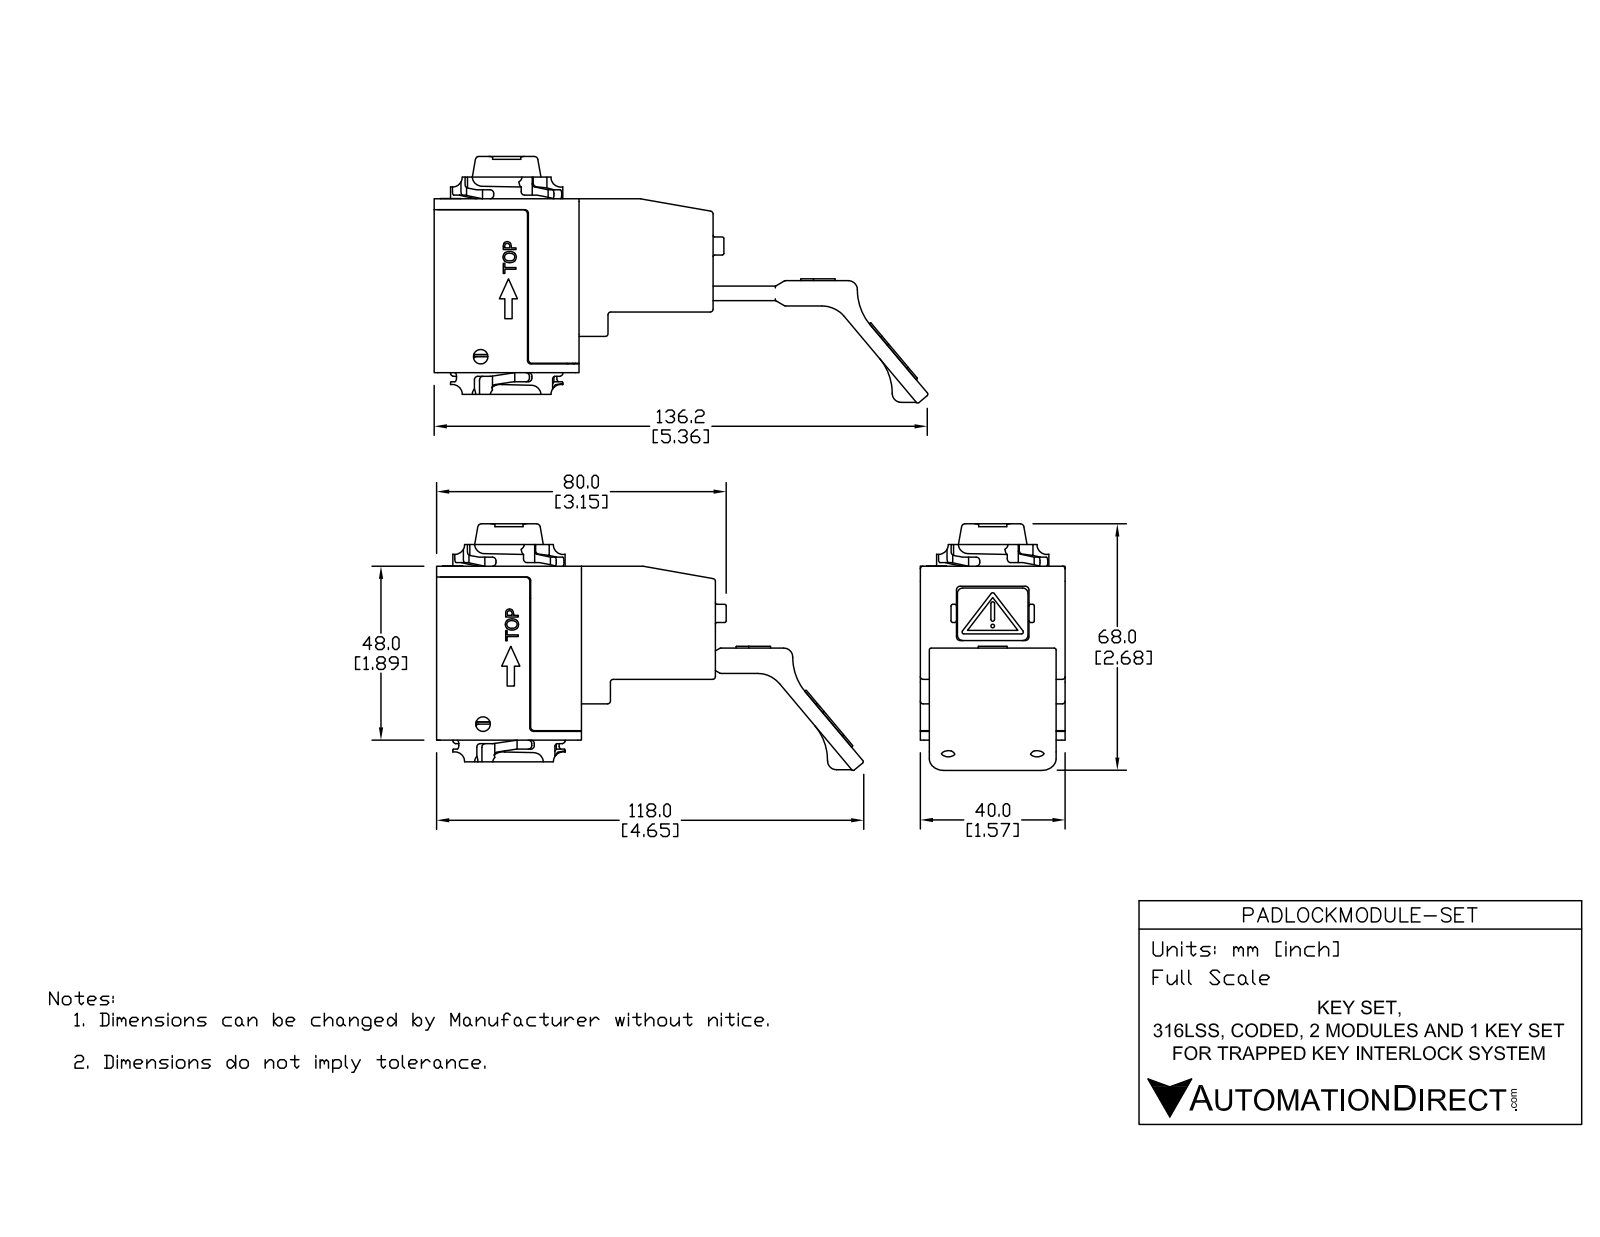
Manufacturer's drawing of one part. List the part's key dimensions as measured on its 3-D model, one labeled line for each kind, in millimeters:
Part name (STEP PRODUCT): ST2330_Bajonett; ST2140_V; PADLOCKMODULE-SET
STEP written by: SolidWorks 2017 (AUTOMOTIVE_DESIGN)
Units: millimetres
Bodies: 2 solids, 1446 faces (641 planar, 209 cylindrical, 596 other)
Overall size (bounding box): 119.2 × 65 × 40.3
Volume: 145 100 mm³ · Surface area: 27 570 mm²
Round holes (diameter × count): ⌀4 ×3, ⌀5.5 ×2, ⌀1 ×1, ⌀2 ×1, ⌀2.5 ×1
Round bosses / shafts (diameter × count): ⌀10 ×1
Partial cylindrical surfaces — rounded edges, fillets, slot ends (radius × count): R0.5 ×109, R1 ×22, R0.5 ×18, R0.8 ×17, R1.5 ×8, R5.5 ×2, R2 ×1, R3 ×1
Main face-to-face distances: 40, 48, 60, 12, 16.7, 31.2, 43.3, 4, 6.8, 10
Hole centre spacings: 14.5, 18, 23.1, 24.5, 30
